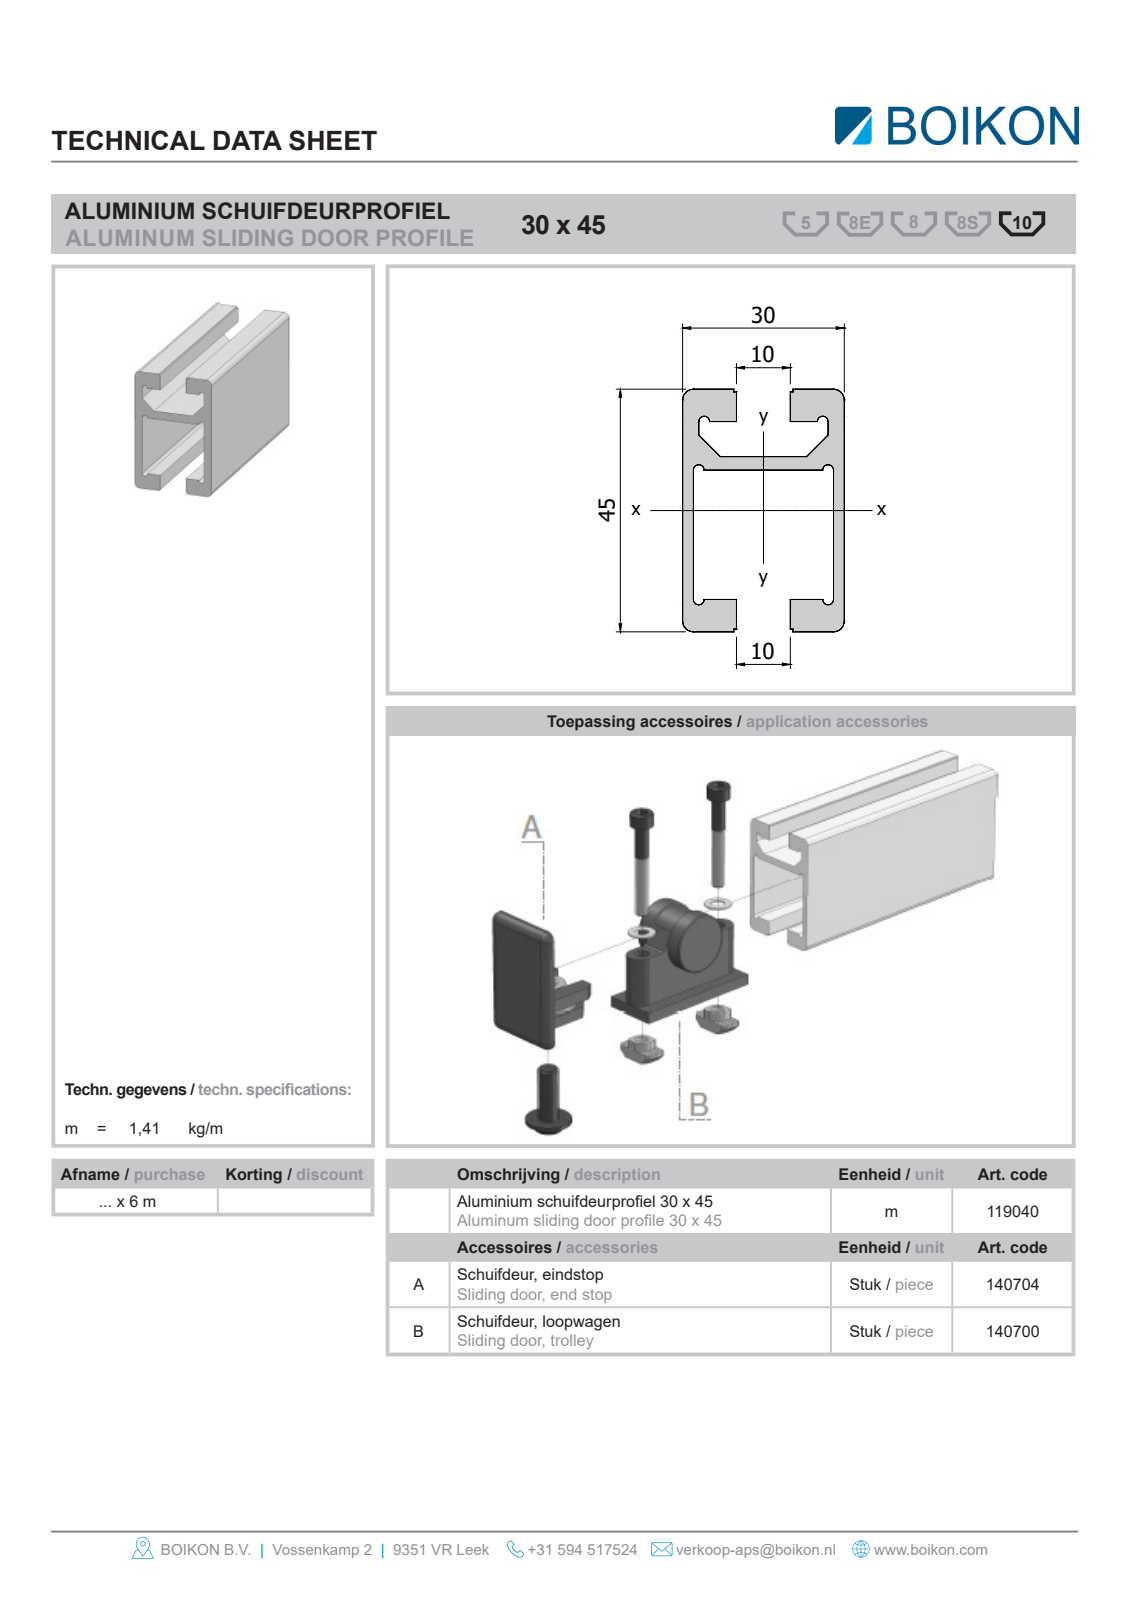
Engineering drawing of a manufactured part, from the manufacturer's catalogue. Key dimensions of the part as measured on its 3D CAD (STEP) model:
Part name (STEP PRODUCT): Root; 119040SCHUIFDPROFIEL 30X45BOIKON0
STEP written by: HiCAD 2013 1802.4 Build 509 (AUTOMOTIVE_DESIGN)
Units: millimetres
Bodies: 1 solid, 42 faces (32 planar, 10 cylindrical, 0 other)
Overall size (bounding box): 1000 × 45 × 30
Volume: 452 142 mm³ · Surface area: 294 634 mm²
Partial cylindrical surfaces — rounded edges, fillets, slot ends (radius × count): R1 ×6, R2 ×4
Main face-to-face distances: 30, 2, 28, 10, 26, 6, 39, 20, 8, 18
